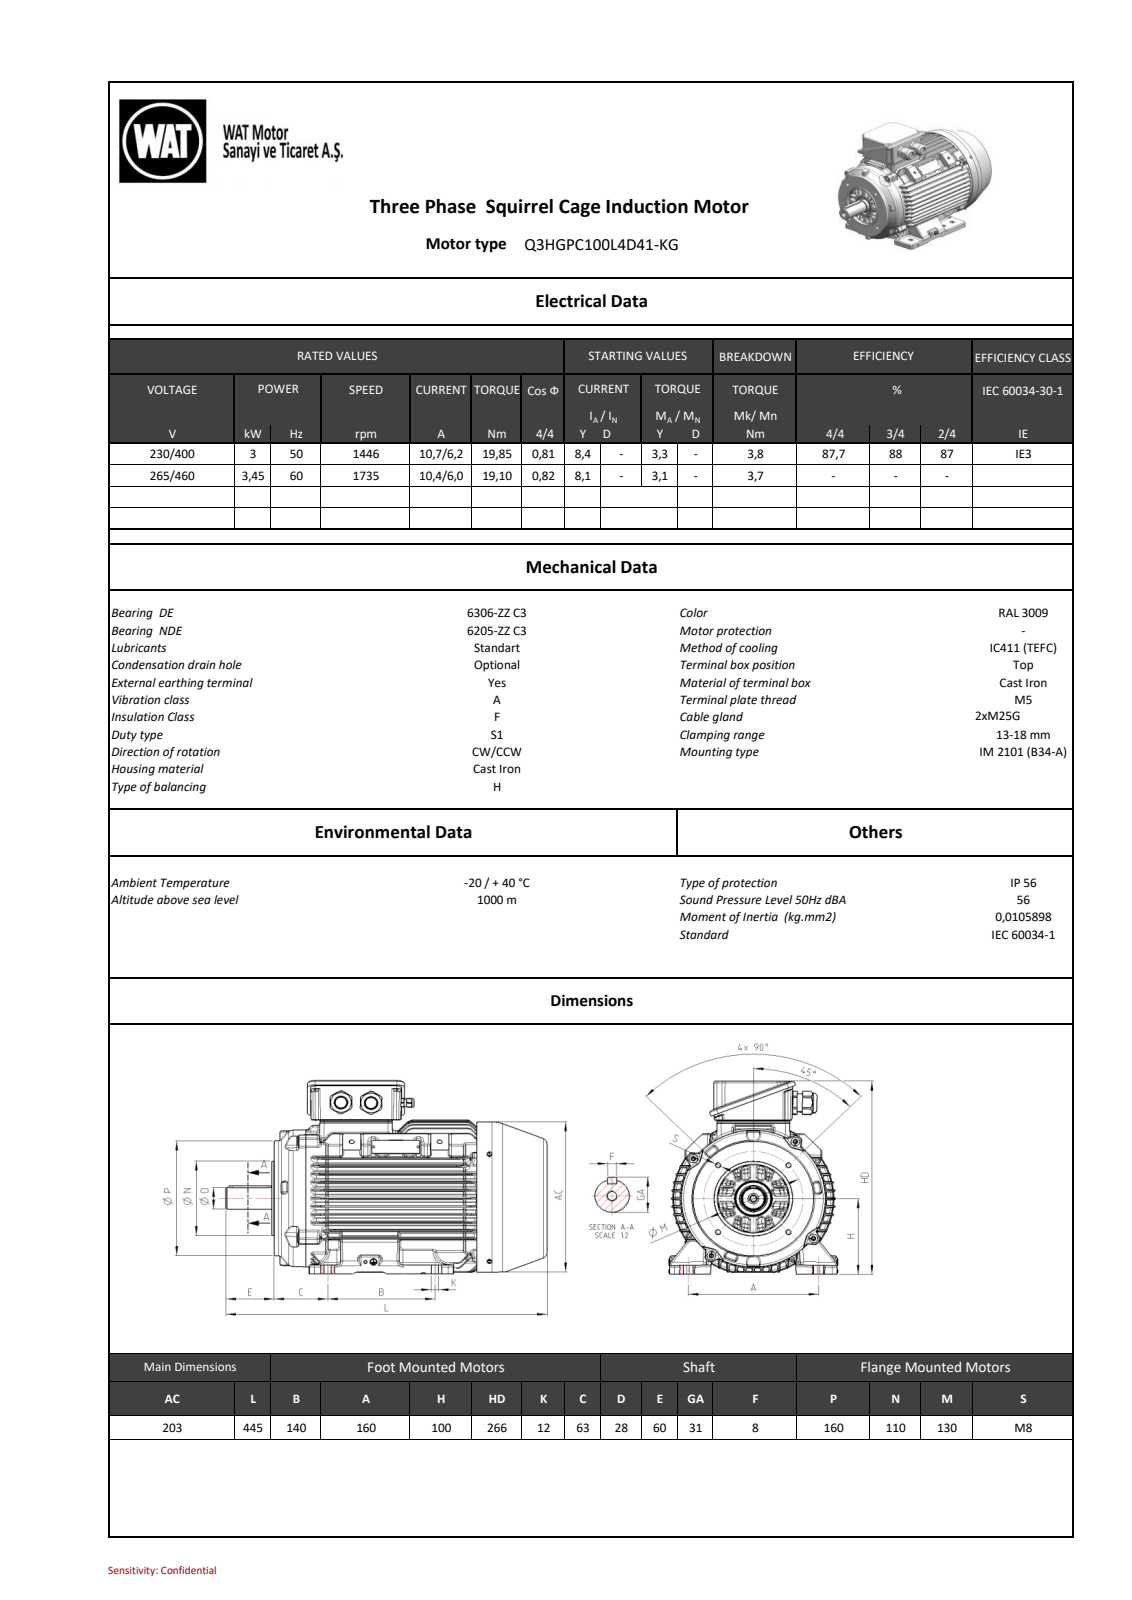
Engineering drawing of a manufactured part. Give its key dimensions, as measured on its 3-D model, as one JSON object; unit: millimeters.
{"part_name": "26000A30F4D8royd", "step_written_by": "SIEMENS PLM Software NX 11.0 (AUTOMOTIVE_DESIGN)", "units": "millimeters", "bodies": {"solids": 0, "faces": 4579, "planar": 896, "cylindrical": 1215, "other": 2468}, "overall_size": [445, 265.48, 204.29], "round_holes": [[5, 8], [6.8, 6], [10, 3], [17.2, 2], [4.2, 1], [6.5, 1], [8.5, 1], [10.5, 1], [43.4, 1], [43.6, 1], [197, 1]], "round_bosses_or_shafts": [[12, 4], [10, 4], [8.65, 4], [8, 4], [4, 4], [27.7, 2], [25.25, 2], [20, 2]], "partial_cylinders_radius": [[3, 377], [1.5, 124], [2, 48], [1, 37], [0.25, 28], [1.8, 26], [26.5, 12], [34.5, 12]], "face_to_face_distances": [13.52, 13.61, 27.13, 78.72, 51.59, 65.11, 40.83, 27.31, 13.7, 37.89], "hole_center_spacings": [27.87, 89.5, 101.07, 119.39, 126.57, 153.92, 31.07, 65]}
